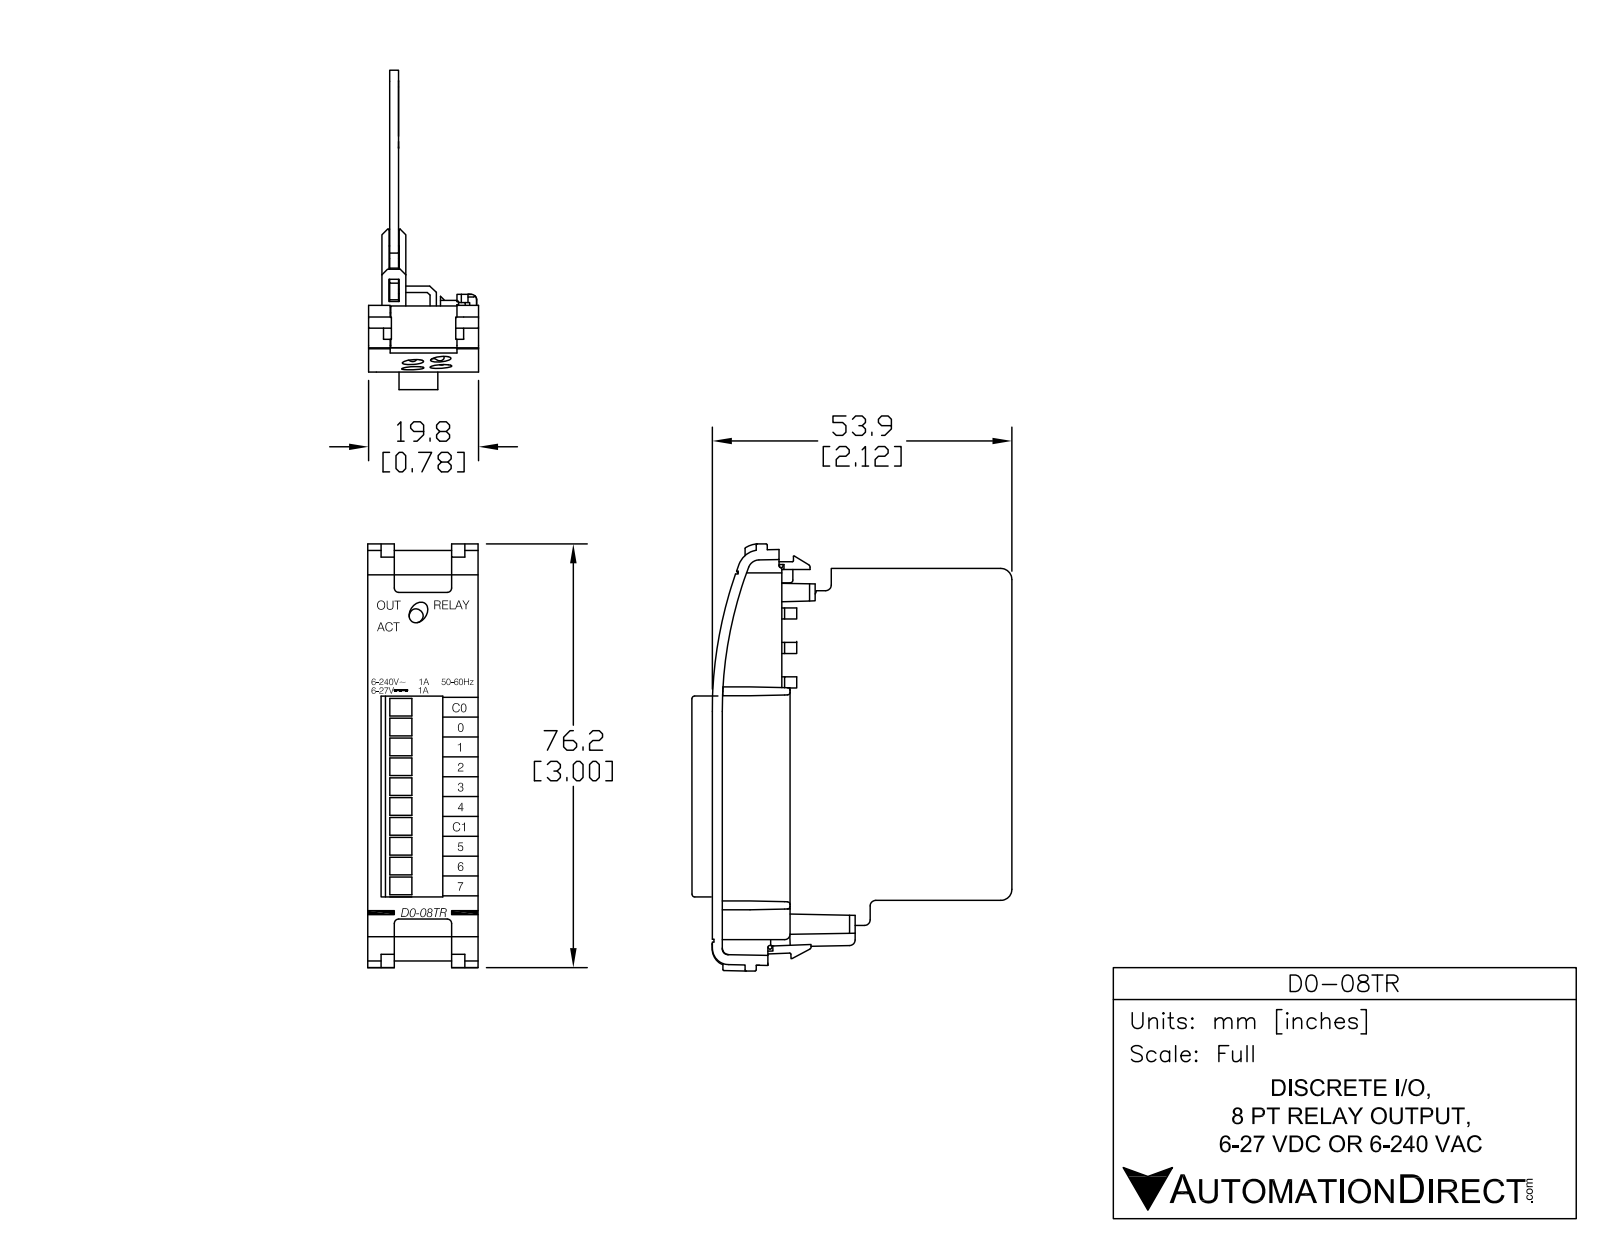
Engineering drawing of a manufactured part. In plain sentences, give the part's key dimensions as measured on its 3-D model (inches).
The part is named "D0-08TR". Its 3-D file was written by "SolidWorks 2009 (AUTOMOTIVE_DESIGN)". It is 2 solids with 328 faces: 241 planar, 38 cylindrical and 49 other. Overall it measures 3.08 by 2.602 by 0.826 inches. Its volume is 0.756 cubic inches and its surface area 23.26 square inches. Round bosses or shafts: 1 of diameter 0.089. Partial cylindrical surfaces (rounded edges, fillets, slot ends): 4 of radius 0.005, 3 of radius 0.02, 3 of radius 0.035, 2 of radius 0.025, 1 of radius 0.01, 1 of radius 0.065, 1 of radius 0.07, 1 of radius 0.1. The main face-to-face distances are 0.063, 0.631, 0.05, 0.075, 0.581, 0.519, 0.113, 0.681, 0.569, 0.195.
